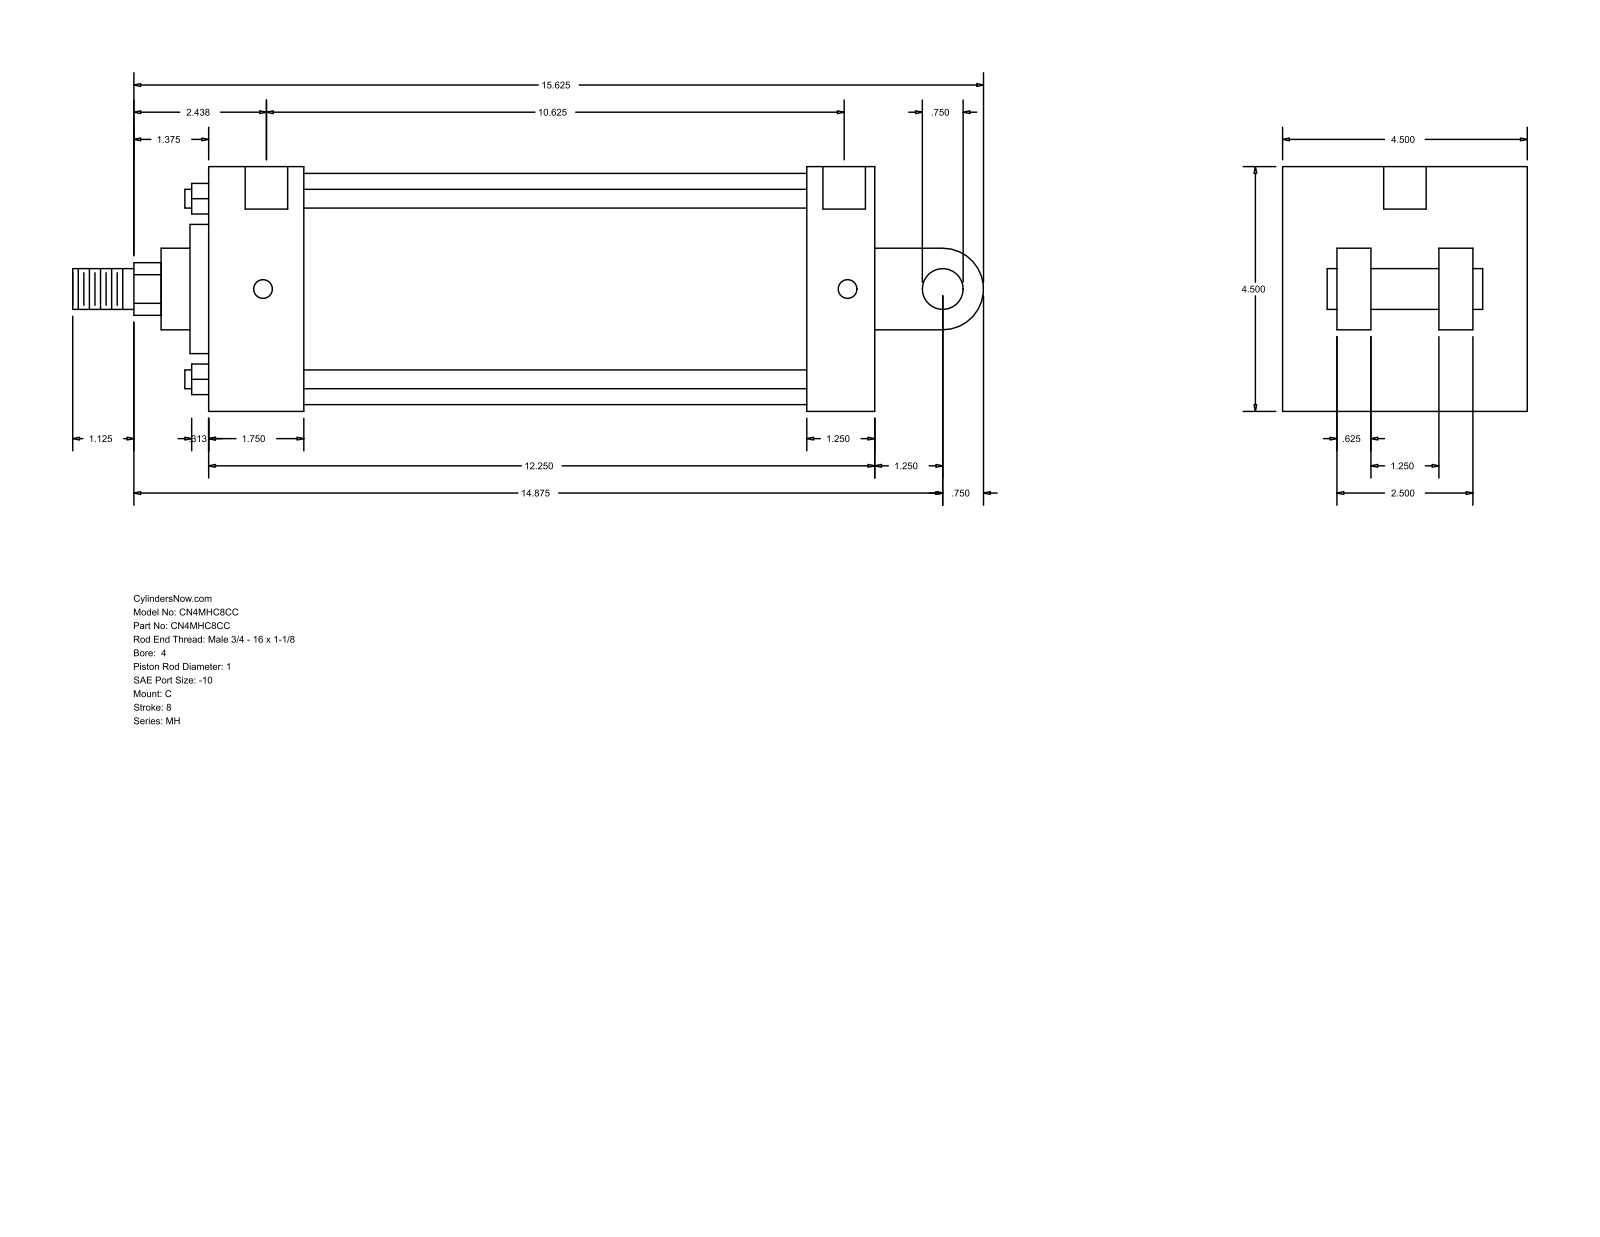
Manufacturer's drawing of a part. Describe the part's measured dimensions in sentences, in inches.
The part is named "MH_C__0400_1". Its 3-D file was written by "GSSL Pune (CONFIG_CONTROL_DESIGN)". It is 0 solids with 101 faces: 71 planar, 30 cylindrical and 0 other. Overall it measures 16.75 by 4.5 by 4.5 inches. Round holes: 4 of diameter 0.344, 2 of diameter 0.781. Round bosses or shafts: 4 of diameter 0.345, 2 of diameter 0.75, 1 of diameter 4.25, 1 of diameter 2.375, 1 of diameter 1.5, 1 of diameter 1. Partial cylindrical surfaces (rounded edges, fillets, slot ends): 1 of radius 0.484, 1 of radius 0.75. The main face-to-face distances are 4.5, 12.25, 1.75, 11, 9.25, 10.5, 1.25, 2.875, 1.625, 1.5. The hole center spacings are 10.75, 0.062, 0.063, 10.625, 10.687, 10.688.
